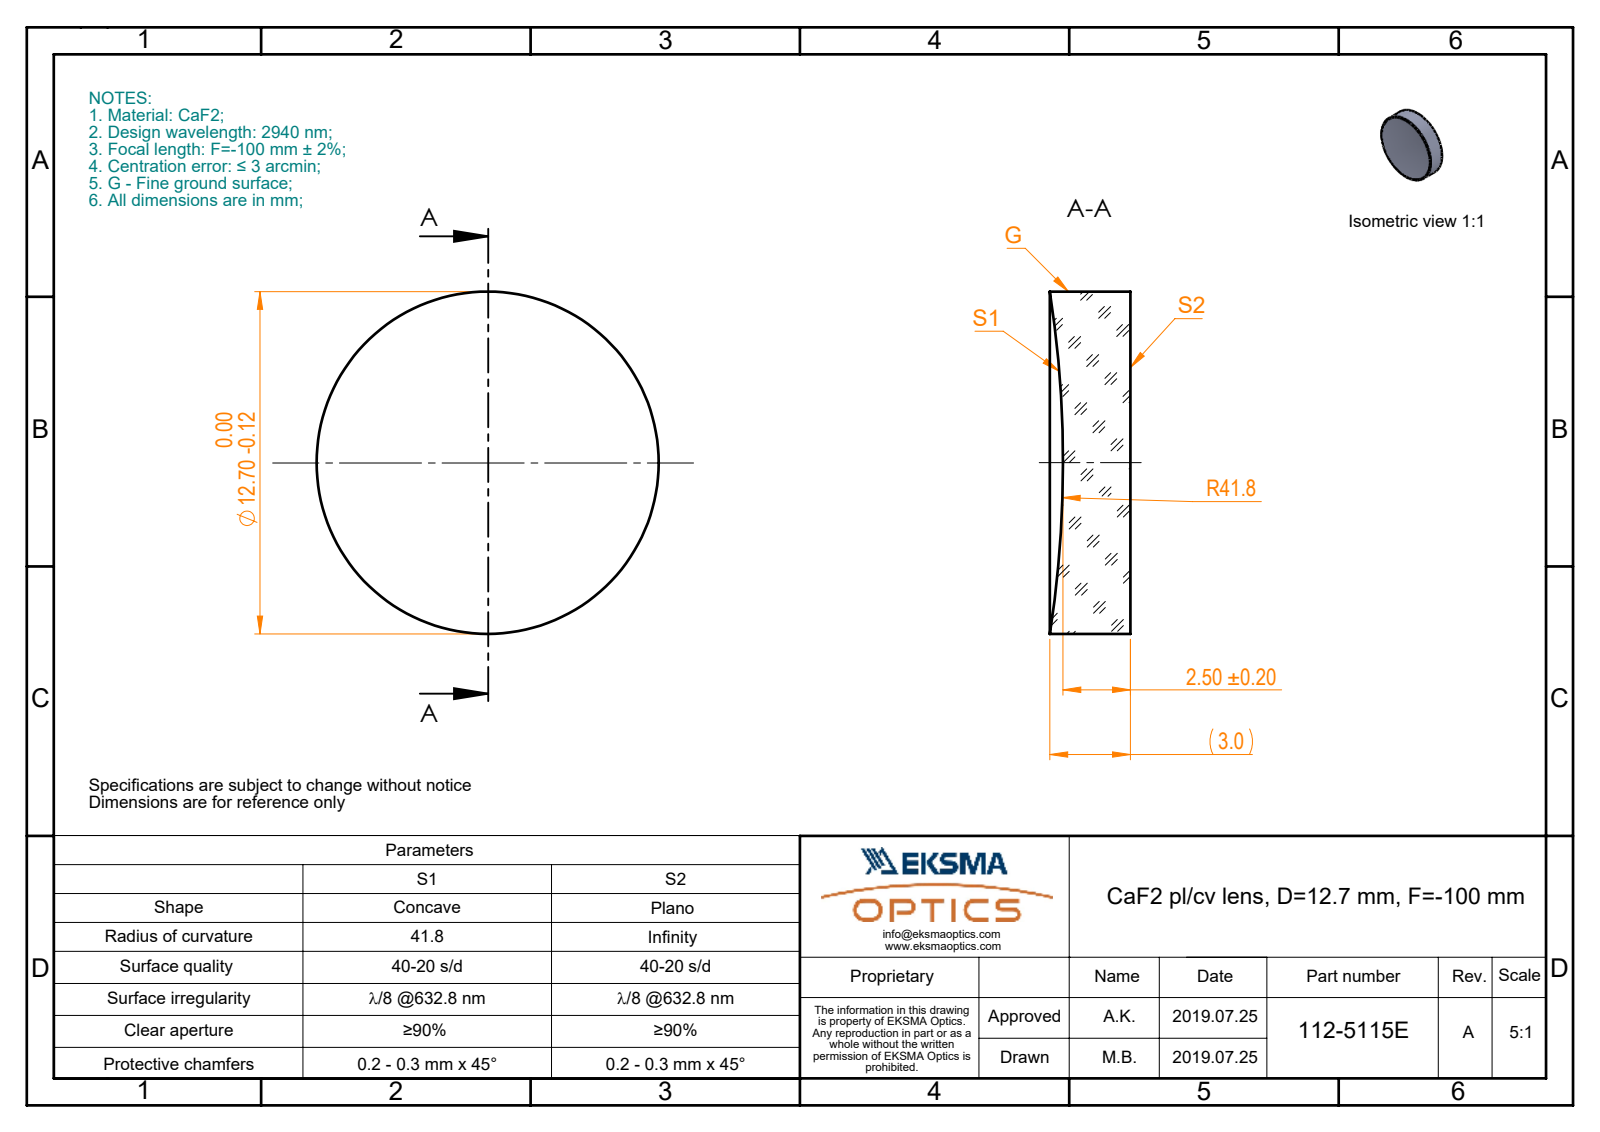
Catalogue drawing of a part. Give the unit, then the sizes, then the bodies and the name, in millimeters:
Units: millimetres
Overall size (bounding box): 12.7 × 12.7 × 2.98
Round bosses / shafts (diameter × count): ⌀12.7 ×1
Volume: 347 mm³ · Surface area: 373 mm²
Bodies: 1 solid, 5 faces (1 planar, 2 cylindrical, 2 other)
Part name (STEP PRODUCT): 112-5115E CaF2 pl-cv 12.7 F-100
STEP written by: SolidWorks 2017 (CONFIG_CONTROL_DESIGN)
